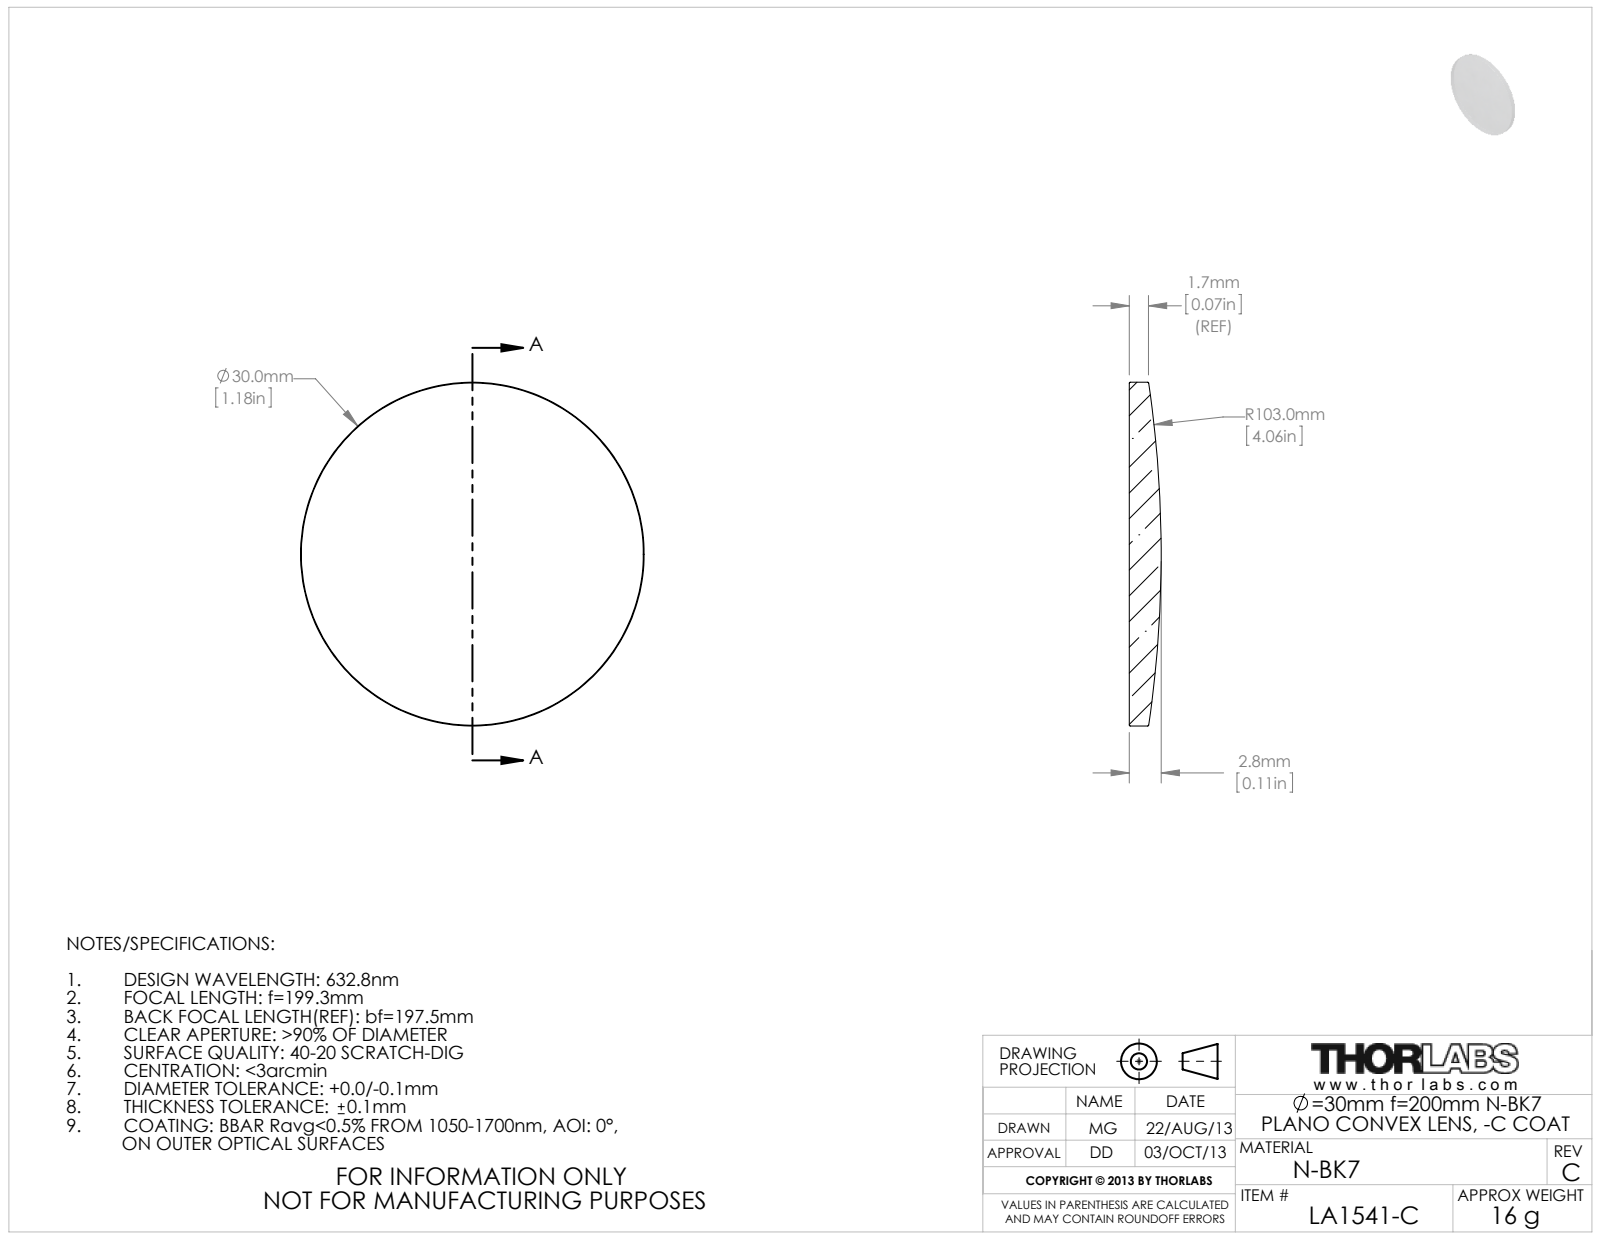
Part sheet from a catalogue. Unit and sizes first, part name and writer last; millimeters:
Units: millimetres
Overall size (bounding box): 30 × 30 × 2.78
Round bosses / shafts (diameter × count): ⌀30 ×1
Volume: 1 578 mm³ · Surface area: 1 576 mm²
Bodies: 1 solid, 5 faces (1 planar, 2 cylindrical, 2 other)
Part name (STEP PRODUCT): 19312-E0W
STEP written by: SolidWorks 2009 (AUTOMOTIVE_DESIGN)
